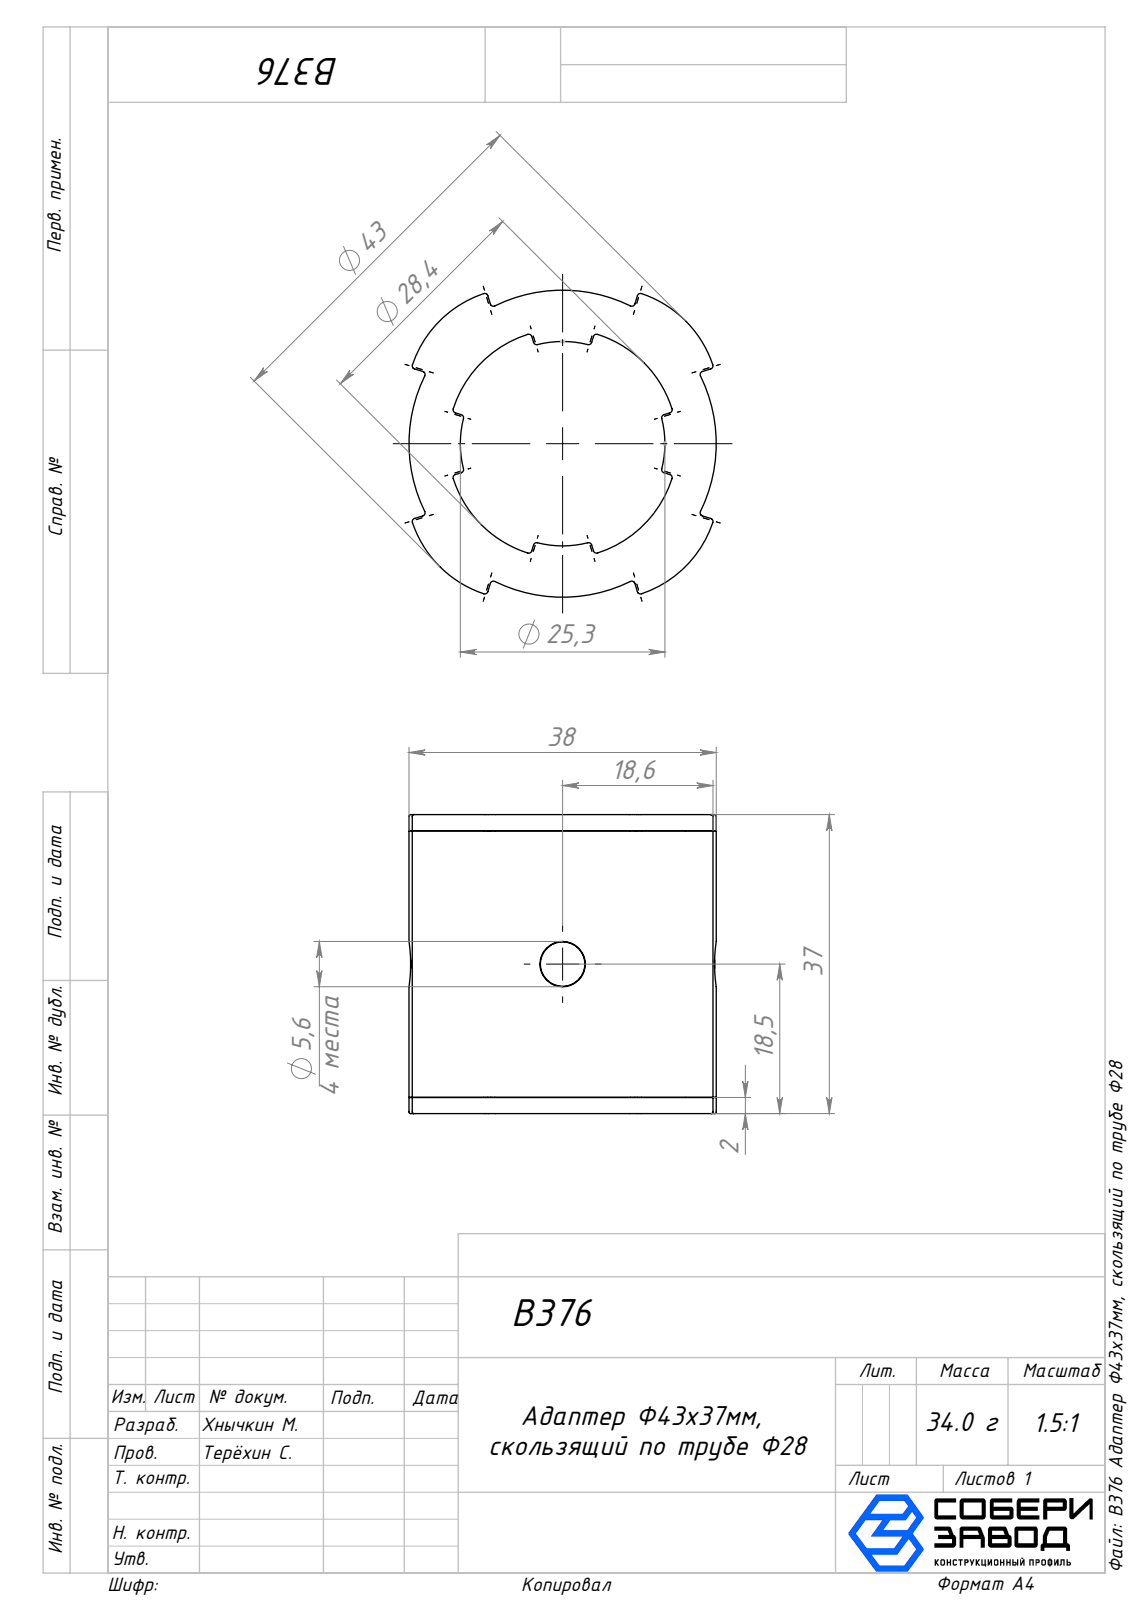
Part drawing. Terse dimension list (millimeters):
name: Корпус_00; Крышка_00; B376 Адаптер Ф43х37мм, скользящий по трубе Ф28
written by: SolidWorks 2025 (AUTOMOTIVE_DESIGN)
unit: mm
bodies: 3 solids, 640 faces (176 planar, 360 cylindrical, 104 other)
size: 38.4 × 38 × 37
volume: 17 015 mm³; area: 18 706 mm²
holes: 2× ⌀5.6, 2× ⌀30
bosses: 1× ⌀5.5
rounds: 80× R0.4, 40× R0.5, 32× R0.2, 16× R0.35, 16× R0.45, 16× R1, 12× R14, 3× R19
face distances: 2, 35, 33, 37, 11, 24, 13, 22, 20.59, 9.5
hole spacings: 0.4
